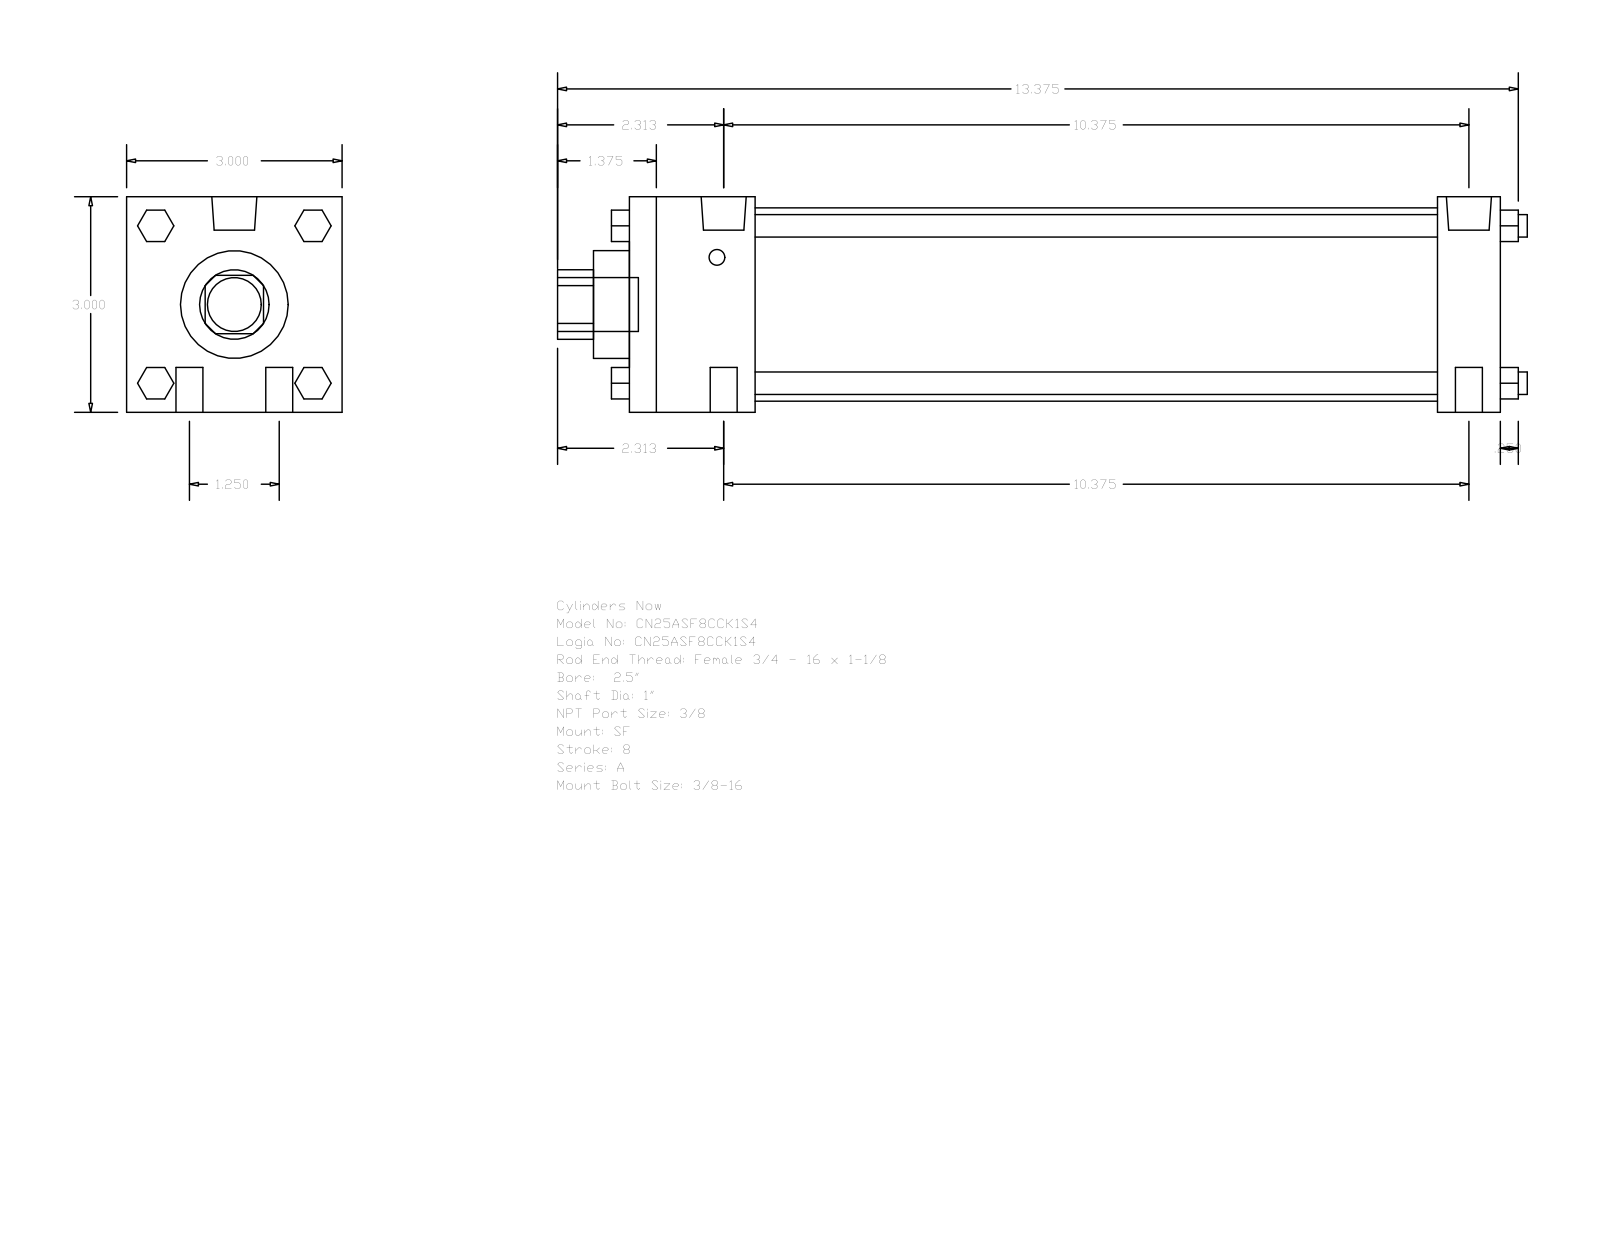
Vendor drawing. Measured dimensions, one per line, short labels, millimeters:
name: A_SF__0250_1
written by: GSSL Pune (CONFIG_CONTROL_DESIGN)
unit: mm
bodies: 0 solids, 124 faces (94 planar, 30 cylindrical, 0 other)
size: 342.9 × 76.2 × 76.2
holes: 1× ⌀25.4, 1× ⌀38.1, 1× ⌀68.33
bosses: 4× ⌀9.53, 4× ⌀7.94, 2× ⌀15.93, 2× ⌀5.56, 1× ⌀19.05
rounds: 1× R12.29
face distances: 76.2, 307.98, 285.75, 22.23, 44.45, 241.3, 263.53, 12.7, 320.68, 6.35
